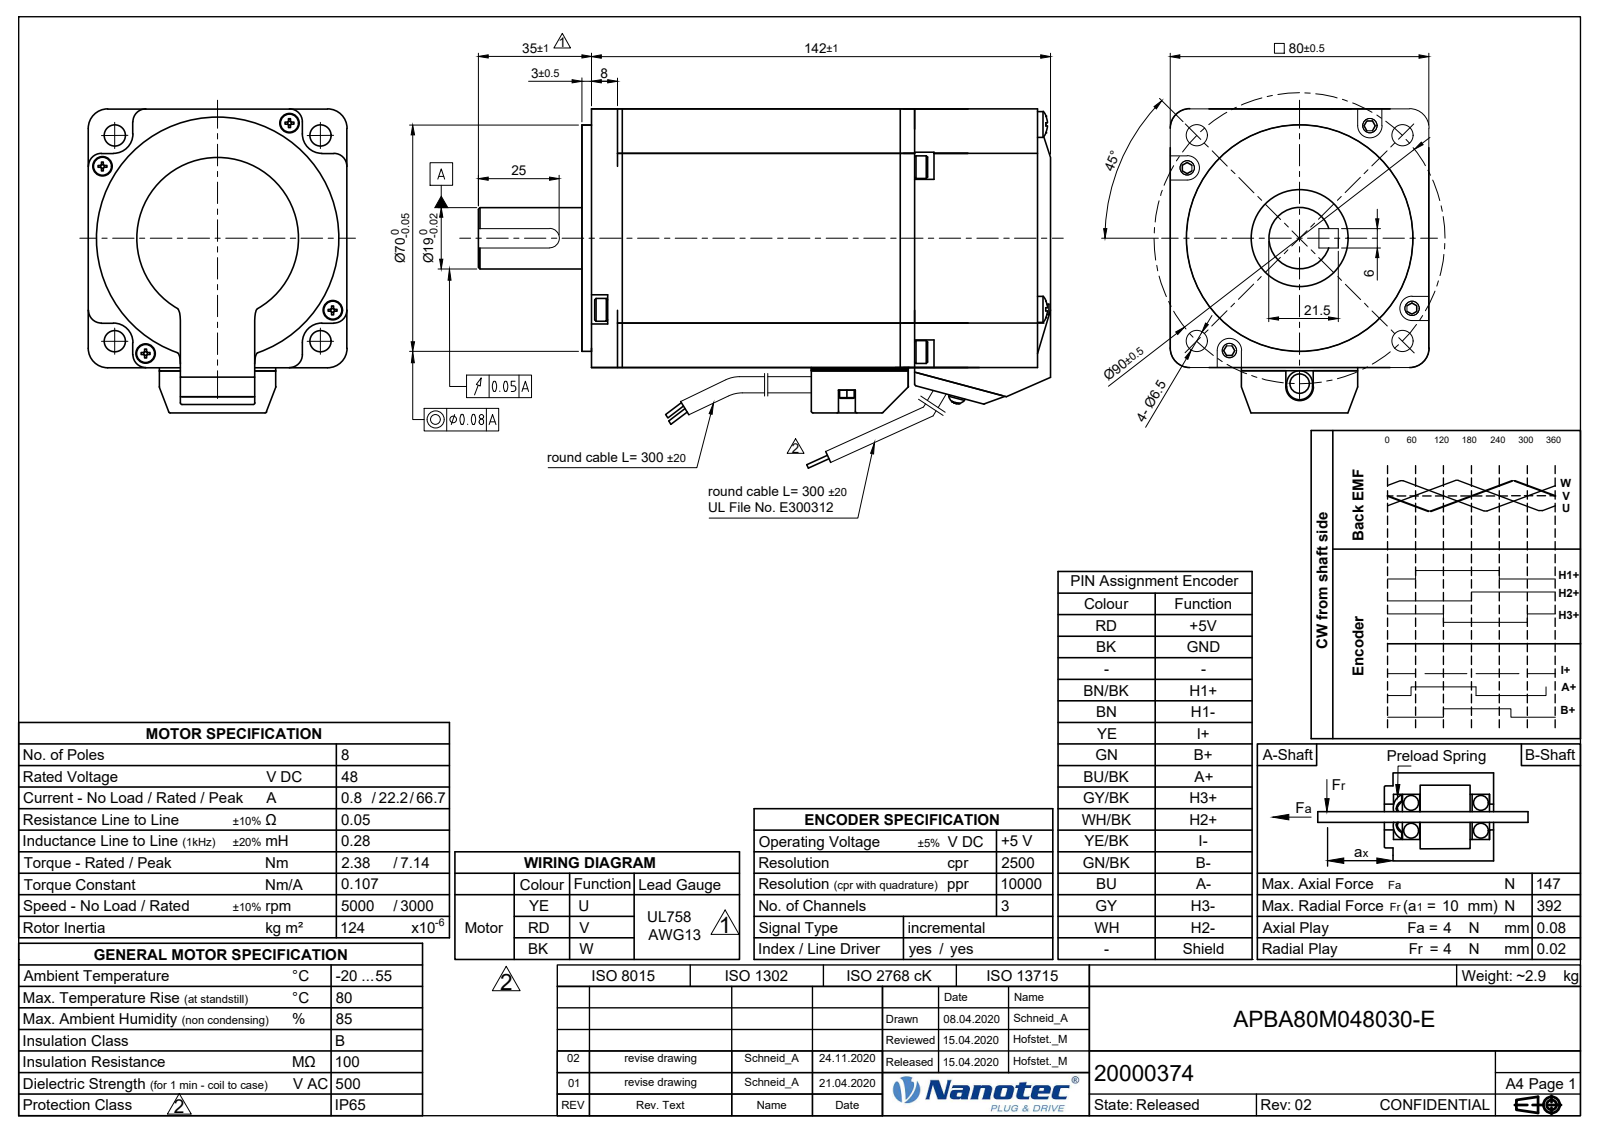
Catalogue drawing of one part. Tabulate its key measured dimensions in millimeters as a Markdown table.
| quantity | value |
| --- | --- |
| part name | APBA80M048030-E_Shrinkwrap_1 |
| STEP written by | Autodesk Inventor 2019 (AUTOMOTIVE_DESIGN) |
| units | millimeters |
| bodies | 37 solids, 2179 faces (1450 planar, 519 cylindrical, 210 other) |
| overall size | 177 × 102.69 × 80 |
| volume | 319 788 mm³ |
| surface area | 168 897 mm² |
| round holes (diameter × count) | 3.3 × 11, 4 × 11, 3 × 10, 0.5 × 8, 2.5 × 6, 2.05 × 5, 6.5 × 5, 2.8 × 4, 3.2 × 4, 3.4 × 4, 4.5 × 4, 1.8 × 2 |
| round bosses / shafts (diameter × count) | 2.7 × 8, 3 × 6, 7 × 4, 6 × 4, 5.6 × 4, 4 × 3, 4.5 × 2, 2.5 × 2 |
| partial cylindrical surfaces (radius × count) | 0.5 × 62, 0.3 × 44, 1 × 20, 0.25 × 16, 4 × 12, 2 × 10, 6 × 8, 3 × 6 |
| main face-to-face distances | 80, 4, 0.5, 4.5, 2.5, 77.5, 11.25, 5, 96, 13.75 |
| hole center spacings | 38.58, 7.65, 10, 10.39, 14.14, 16.07, 18.48, 23.71 |
